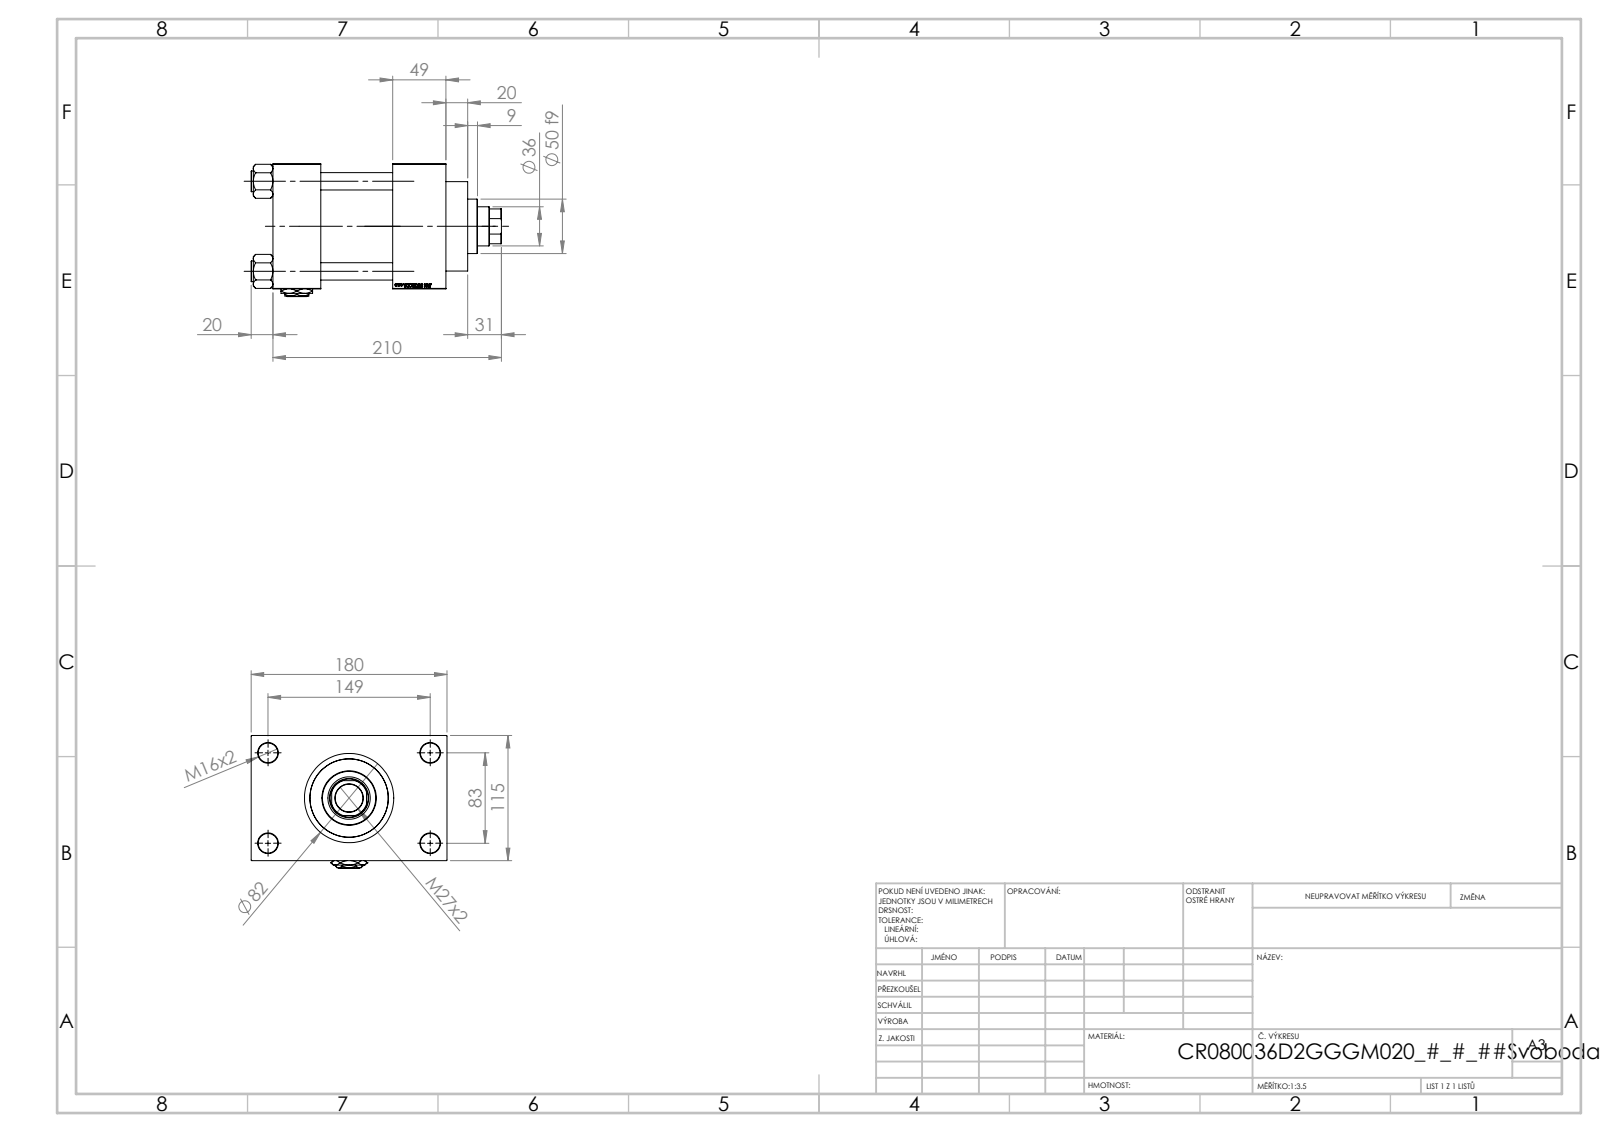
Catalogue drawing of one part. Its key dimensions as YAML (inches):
part_name: "V215_VC_A; NUT_M5_D; V215CR_D_Body; Zatka_pro_OIL_PORT (+2 more)"
step_written_by: "SolidWorks 2019 (CONFIG_CONTROL_DESIGN)"
units: inches
bodies: {solids: 12, faces: 1205, planar: 569, cylindrical: 96, other: 540}
overall_size: [9.055, 7.087, 4.803]
volume: 121.6
surface_area: 461.4
round_holes:
  - {diameter: 0.63, count: 4}
  - {diameter: 0.709, count: 4}
  - {diameter: 0.276, count: 2}
  - {diameter: 1.041, count: 2}
  - {diameter: 1.378, count: 2}
  - {diameter: 1.004, count: 1}
  - {diameter: 1.417, count: 1}
  - {diameter: 1.535, count: 1}
  - {diameter: 2.402, count: 1}
  - {diameter: 2.835, count: 1}
  - {diameter: 3.15, count: 1}
round_bosses_or_shafts:
  - {diameter: 0.748, count: 4}
  - {diameter: 3.386, count: 1}
  - {diameter: 3.228, count: 1}
  - {diameter: 1.969, count: 1}
partial_cylinders:
  - {radius: 0.689, count: 1}
face_to_face_distances: [4.528, 2.598, 4.331, 1.929, 1.732, 6.26, 1.28, 5.807, 0.787, 2.717]
hole_center_spacings: [1.305, 2.302, 3.256, 3.357, 3.513, 4.561, 5.607, 3.268]
